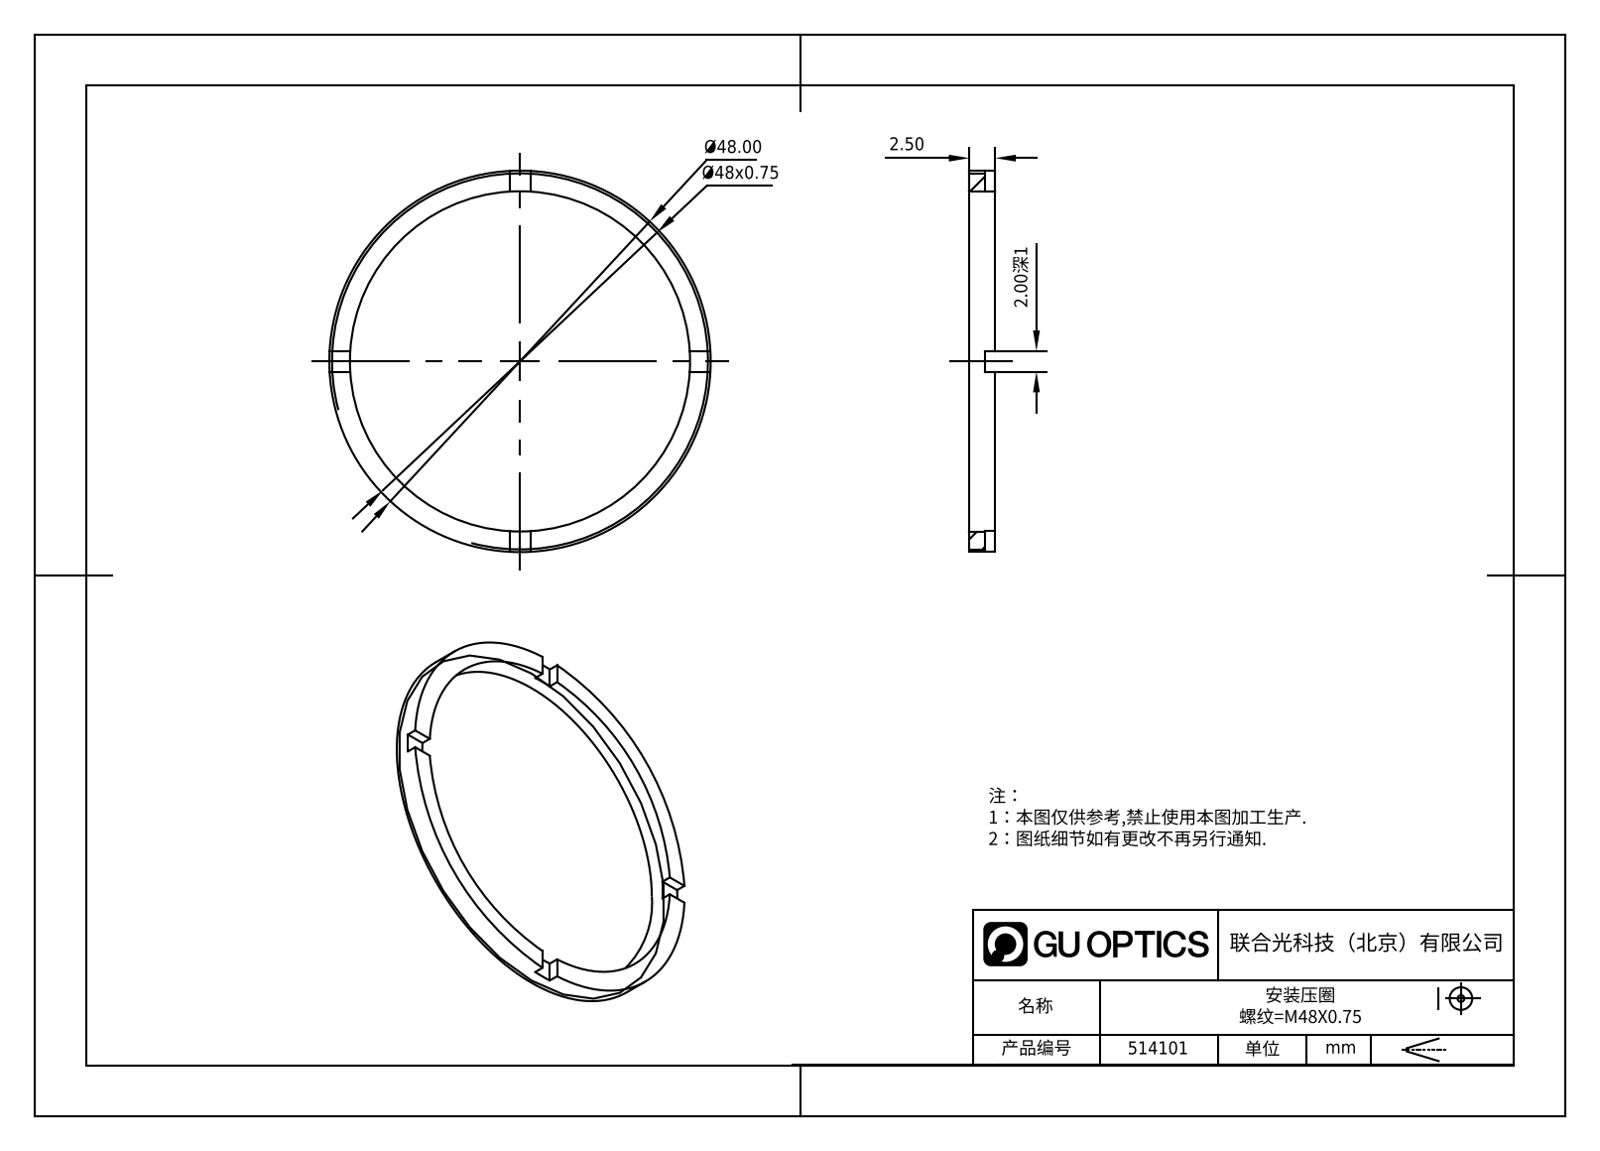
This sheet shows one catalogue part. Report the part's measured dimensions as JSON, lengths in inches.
{"part_name": "514101", "step_written_by": "SolidWorks 2020 (CONFIG_CONTROL_DESIGN)", "units": "inches", "bodies": {"solids": 1, "faces": 21, "planar": 17, "cylindrical": 4, "other": 0}, "overall_size": [1.89, 1.89, 0.098], "volume_in3": 0.043, "surface_area_in2": 2.017, "round_holes": [[1.732, 1]], "round_bosses_or_shafts": [[1.89, 1]], "face_to_face_distances": [0.098, 0.059, 0.039, 0.079]}
